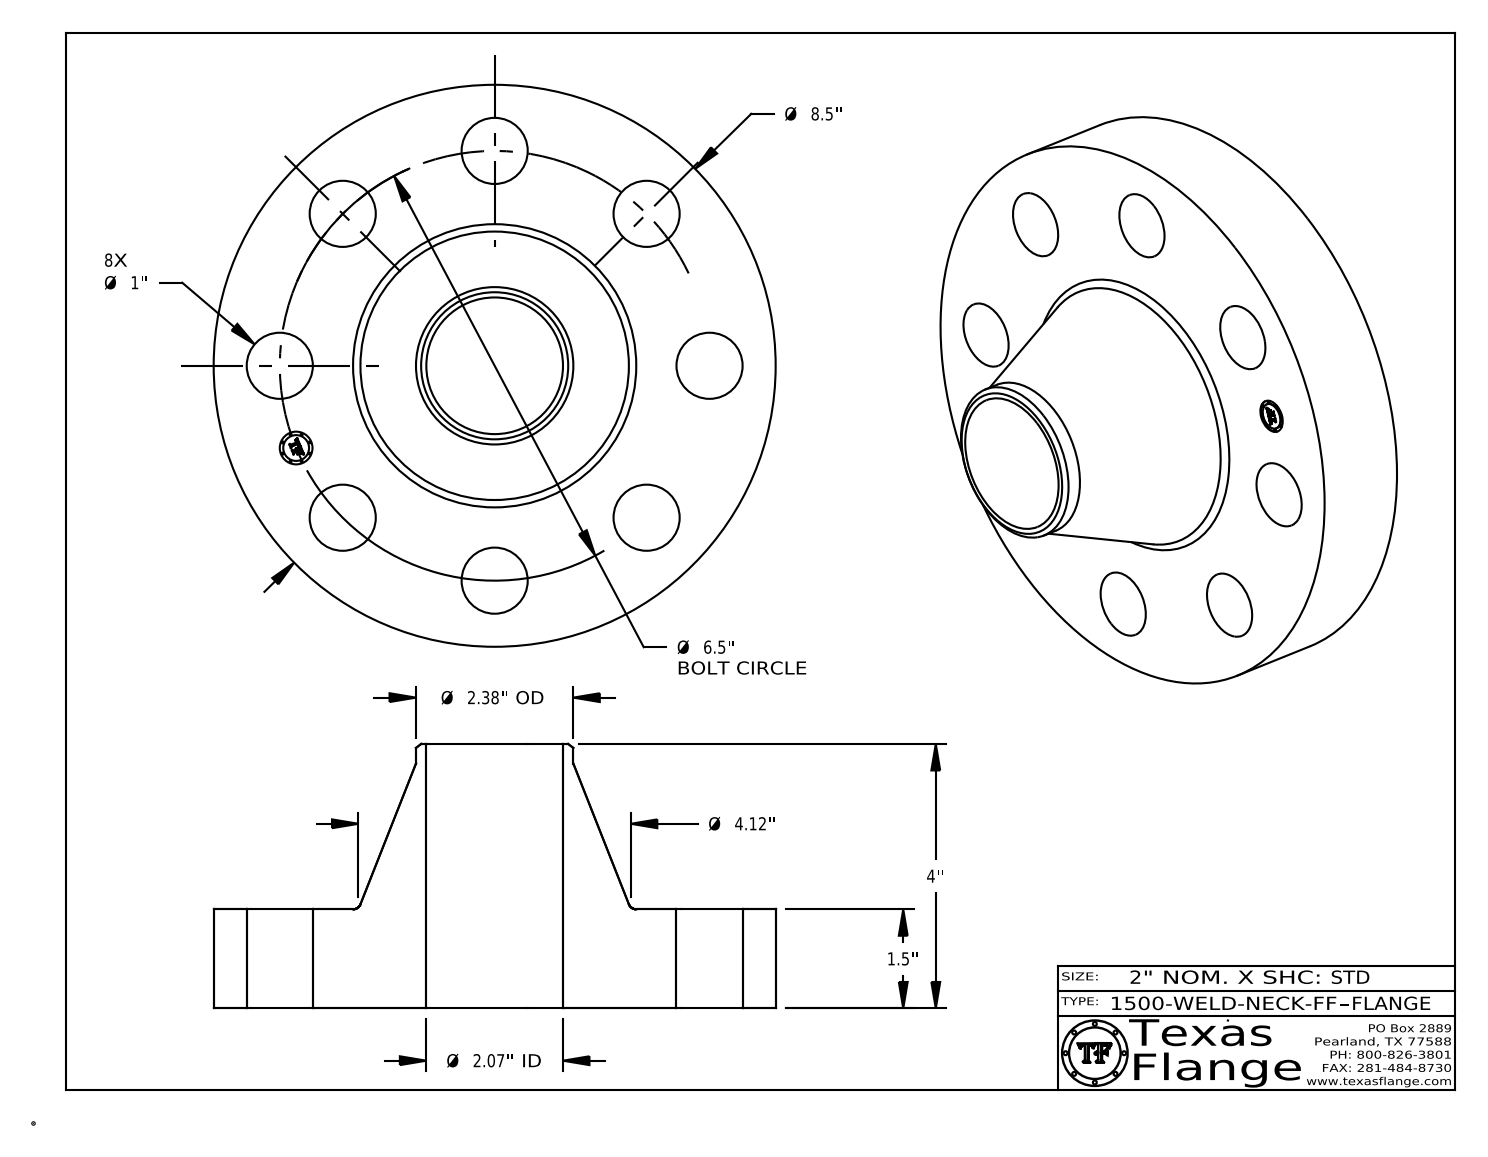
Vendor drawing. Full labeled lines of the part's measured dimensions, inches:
Part name (STEP PRODUCT): 1500-WELD-NECK-FF
STEP written by: CATIA V5 STEP AP214 (AUTOMOTIVE_DESIGN)
Units: inches
Bodies: 1 solid, 416 faces (368 planar, 42 cylindrical, 6 other)
Overall size (bounding box): 8.5 × 8.5 × 4
Volume: 82.31 in³ · Surface area: 215 in²
Round holes (diameter × count): ⌀1 ×8, ⌀0.495 ×1, ⌀2.067 ×1
Round bosses / shafts (diameter × count): ⌀0.03 ×8, ⌀8.5 ×1, ⌀2.38 ×1, ⌀0.39 ×1
Main face-to-face distances: 1.5, 4, 2.5, 1.485, 0.015, 2.515, 0.148, 0.144, 0.027, 0.096
Hole centre spacings: 3.25, 2.487, 4.596, 6.005, 6.5, 1.268, 5.405, 6.375
